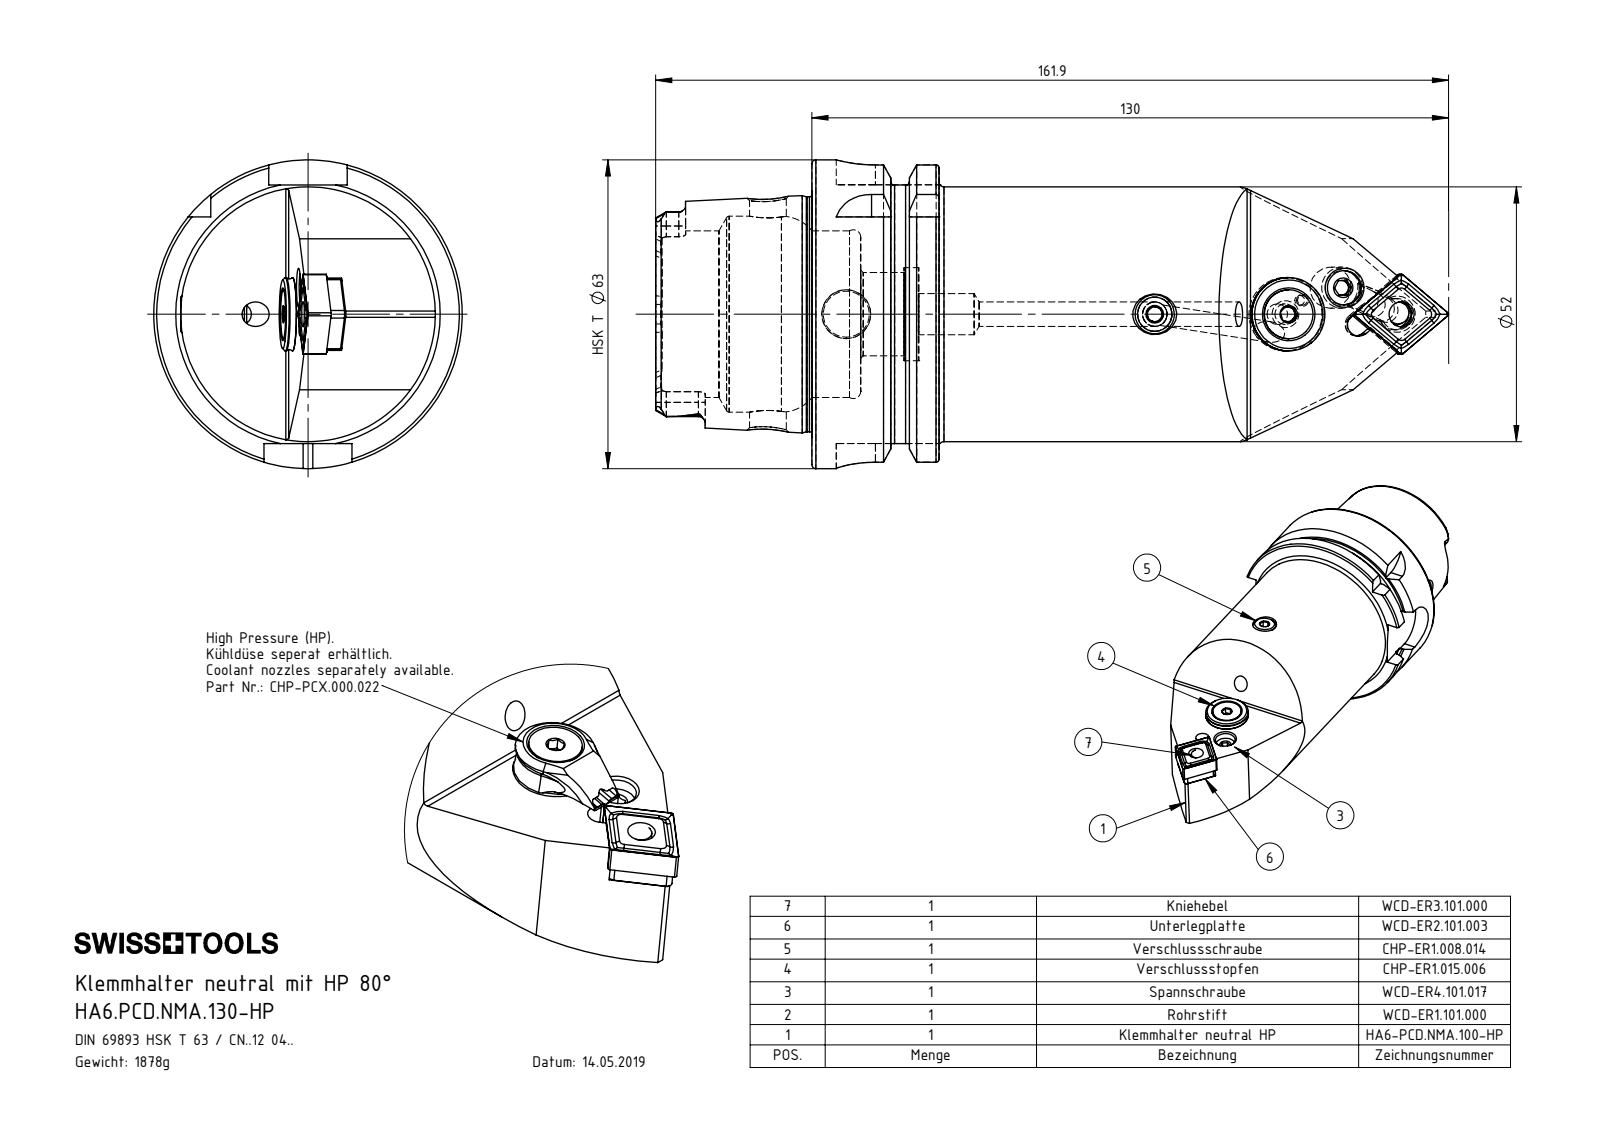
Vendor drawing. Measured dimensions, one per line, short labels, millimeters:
name: DIN 7991 - M5x15; CHP-ER1.015.006_A; PC..NMA.130-HP; HA6-PCD.NMA.130-HP_E (+8 more)
written by: SolidWorks 2017 (AUTOMOTIVE_DESIGN)
unit: mm
bodies: 11 solids, 494 faces (160 planar, 137 cylindrical, 197 other)
size: 161.9 × 63 × 63
volume: 238 240 mm³; area: 42 462 mm²
holes: 3× ⌀5, 2× ⌀4.2, 2× ⌀7, 2× ⌀8.4, 1× ⌀1.2, 1× ⌀2, 1× ⌀2.5, 1× ⌀3, 1× ⌀5.16, 1× ⌀5.2, 1× ⌀6.4, 1× ⌀7.5
bosses: 2× ⌀8, 1× ⌀63, 1× ⌀54.95, 1× ⌀52, 1× ⌀47.94, 1× ⌀15, 1× ⌀13.4, 1× ⌀10
rounds: 6× R1.4, 4× R0.4, 4× R1, 4× R2.88, 4× R8, 3× R2.5, 1× R0.8, 1× R2.1
face distances: 25.95, 16, 9.95, 31.9, 41.85, 57.85, 52.8, 21.8, 11.85, 4.5
hole spacings: 4.5, 4.51, 4.52, 4.53, 8.57, 8.58, 12.8, 12.85
